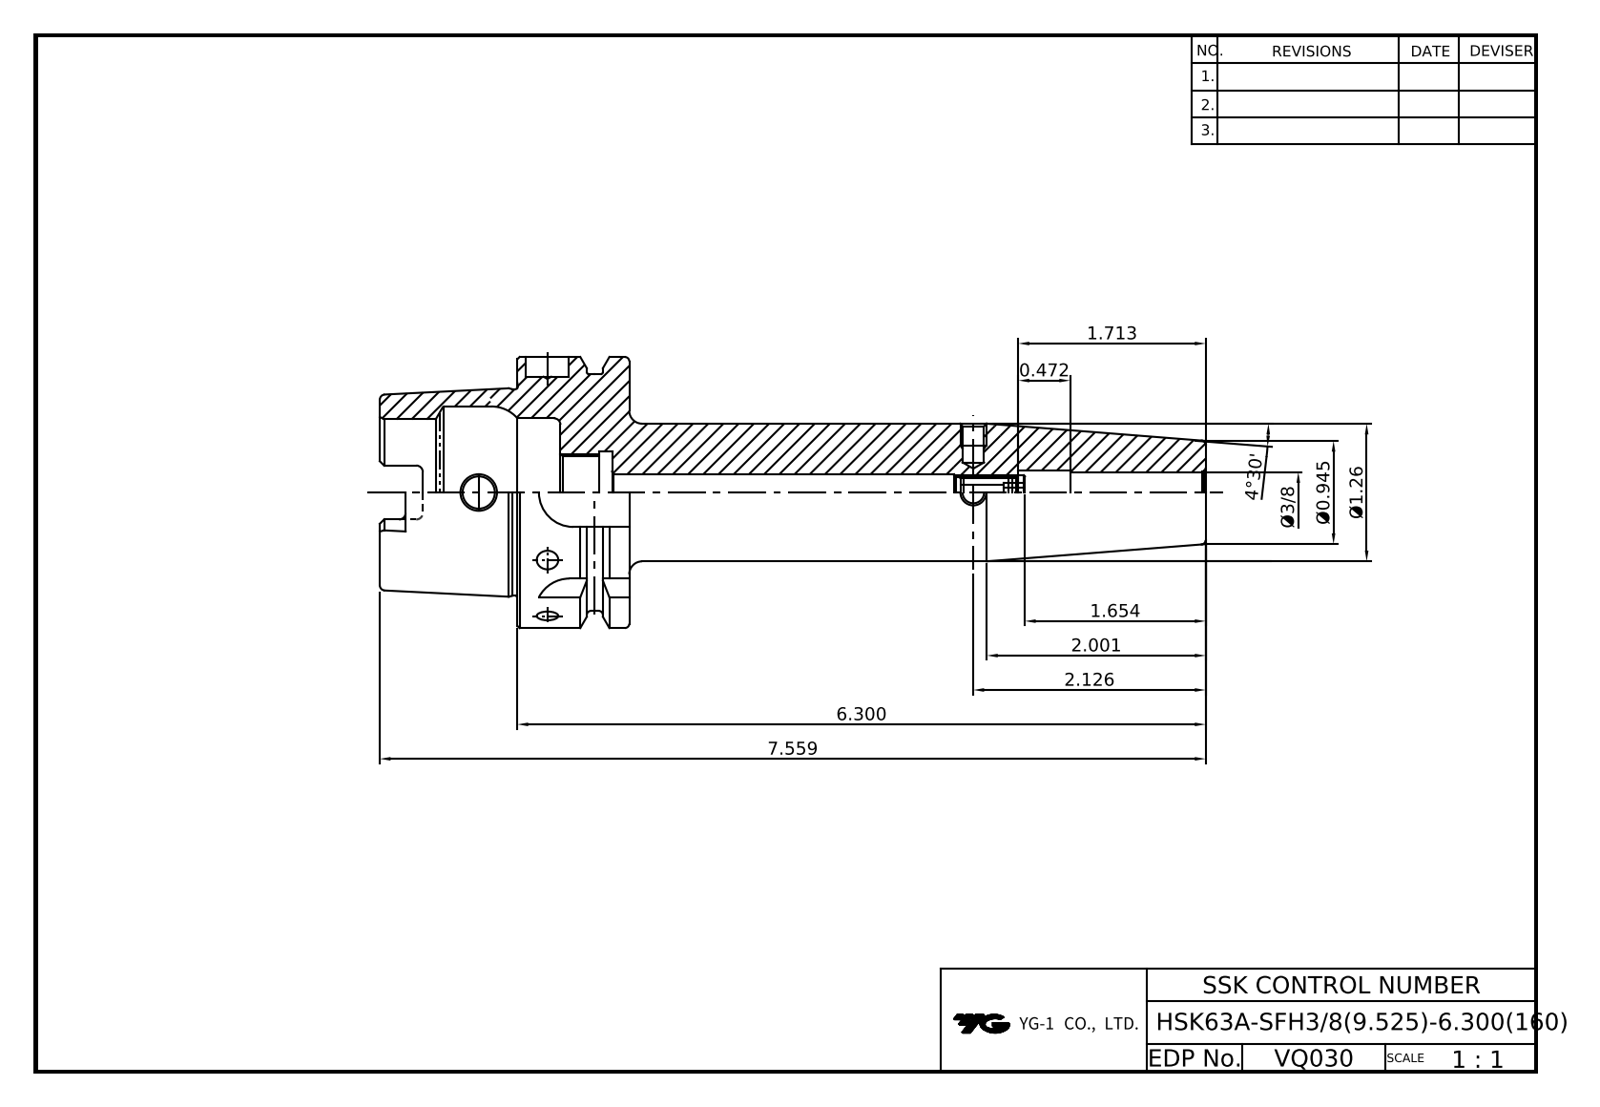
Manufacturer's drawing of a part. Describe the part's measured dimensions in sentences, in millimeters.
The part is named "LO-HSK63A-SFH9.525-160". Its 3-D file was written by "Autodesk Inventor 2022 (AUTOMOTIVE_DESIGN)". It is 1 solid with 114 faces: 42 planar, 33 cylindrical and 39 other. Overall it measures 192 by 63 by 63 millimeters. Its volume is 173 378 cubic millimeters and its surface area 37 987 square millimeters. Round holes: 1 of diameter 6.92, 1 of diameter 7.5, 1 of diameter 9.53, 1 of diameter 10, 1 of diameter 10.73, 1 of diameter 16.92, 1 of diameter 19, 1 of diameter 34, 1 of diameter 40. Round bosses or shafts: 1 of diameter 63, 1 of diameter 55, 1 of diameter 48.04, 1 of diameter 32. Partial cylindrical surfaces (rounded edges, fillets, slot ends): 6 of radius 1.5, 4 of radius 2.88, 4 of radius 8. The main face-to-face distances are 26, 10, 16, 32, 42, 58, 192, 160, 150, 134.
